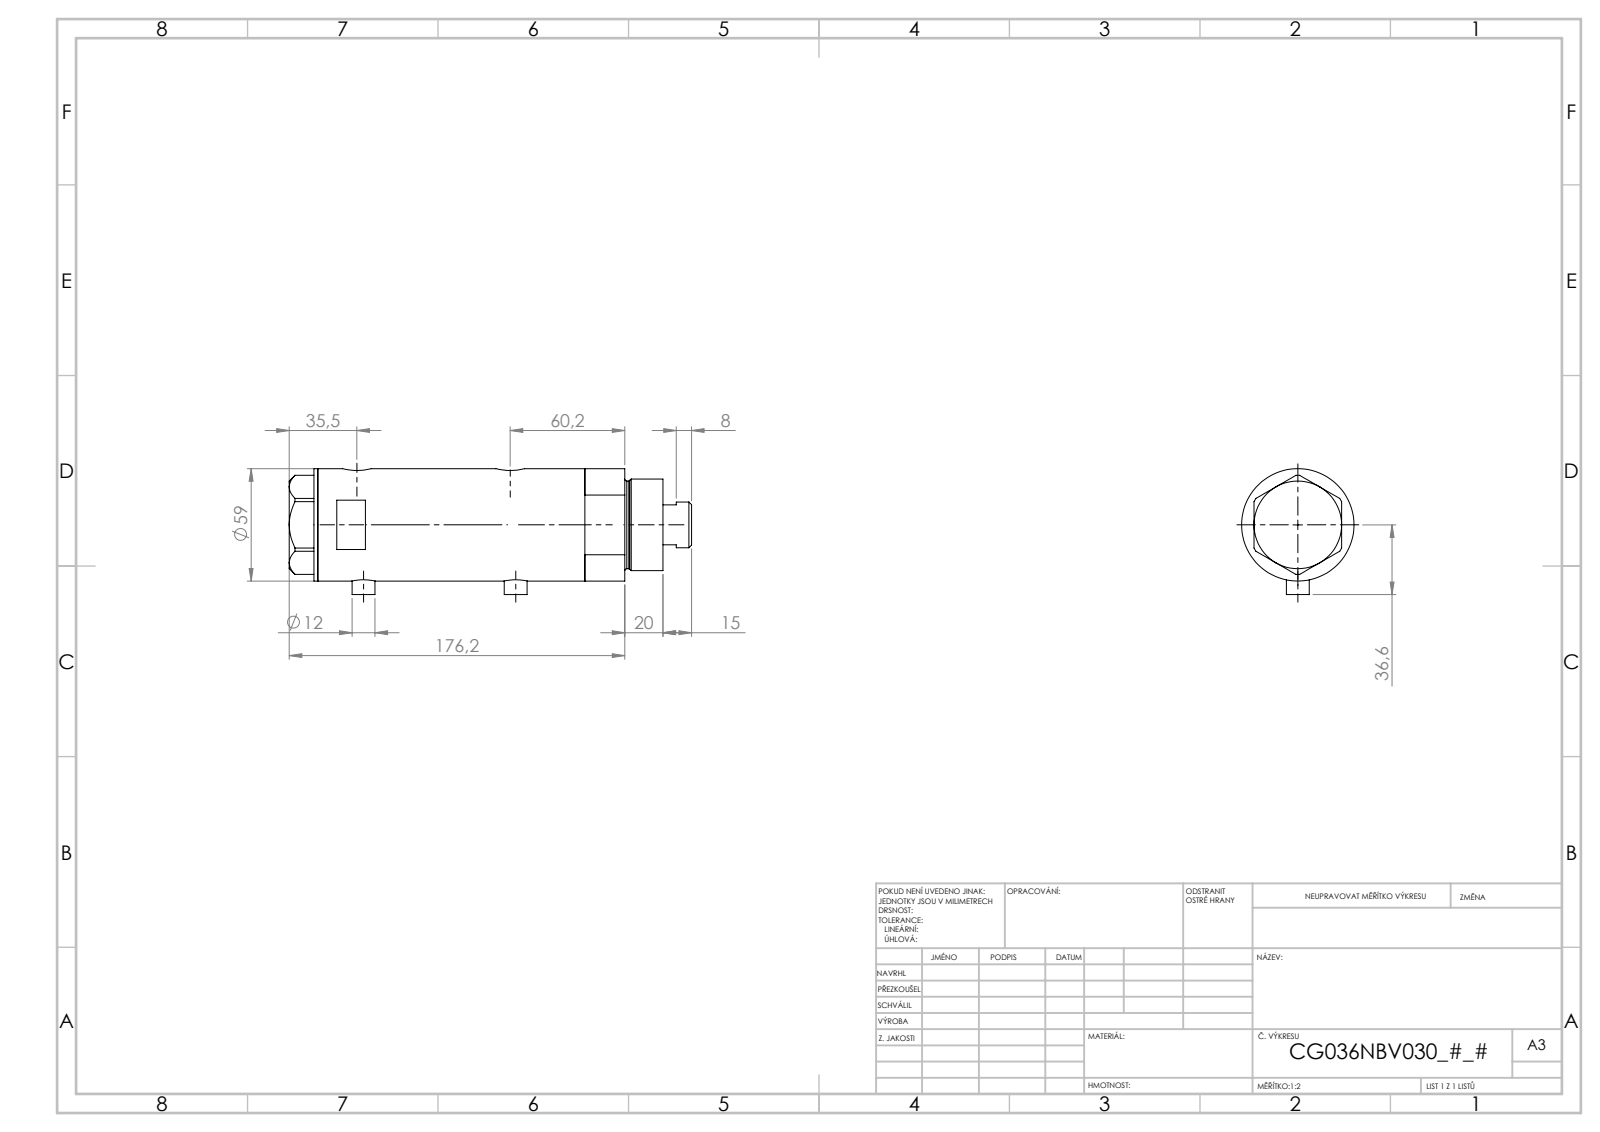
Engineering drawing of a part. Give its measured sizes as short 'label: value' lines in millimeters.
name: V270CG_VC; V270CG_FRONT; V270CG_MIDDLE; V270CG_BACK
written by: SolidWorks 2019 (CONFIG_CONTROL_DESIGN)
unit: mm
bodies: 4 solids, 126 faces (53 planar, 53 cylindrical, 20 other)
size: 193.42 × 60.1 × 59
volume: 437 351 mm³; area: 93 203 mm²
holes: 2× ⌀5, 2× ⌀9.73, 2× ⌀12.5, 2× ⌀15, 1× ⌀8.5, 1× ⌀25, 1× ⌀26.5, 1× ⌀36, 1× ⌀40, 1× ⌀52
bosses: 2× ⌀12, 1× ⌀59, 1× ⌀48, 1× ⌀46, 1× ⌀24
face distances: 87.34, 23.5, 63.84, 15, 38.5, 102.34, 178.42, 163.42, 139.92, 76.08
hole spacings: 2.9, 3.5, 62.15, 65.05, 65.65, 68.55, 2.89, 2.91
